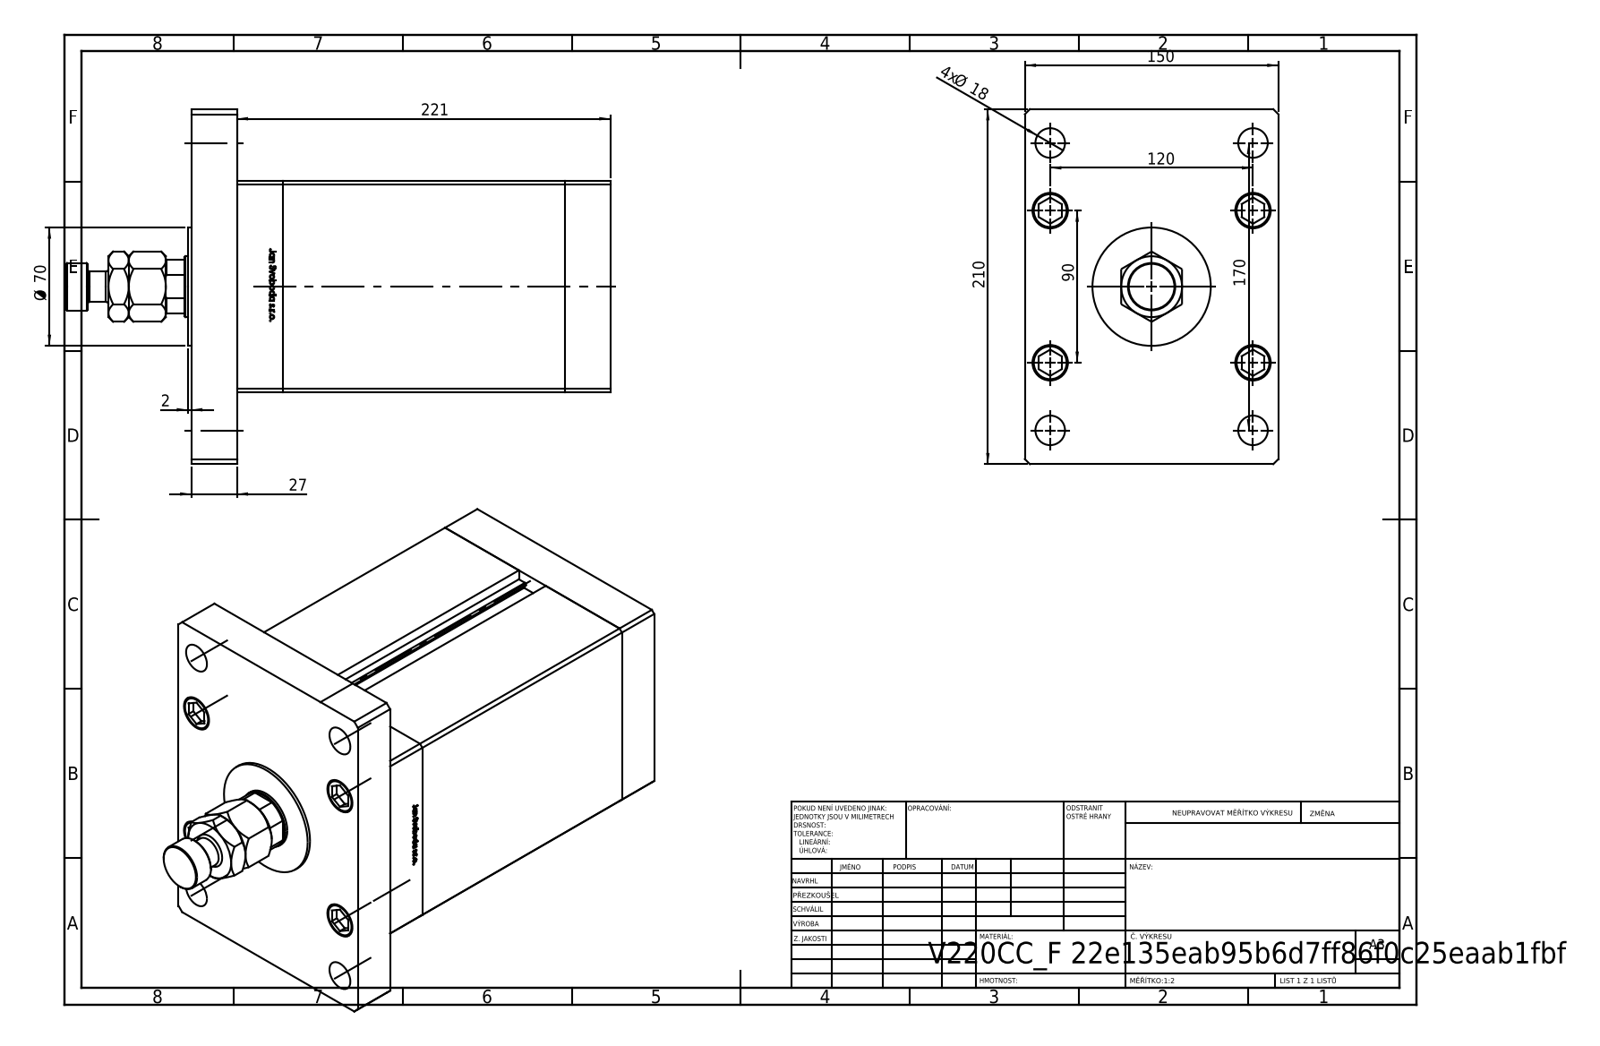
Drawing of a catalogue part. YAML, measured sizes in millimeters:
part_name: "V220C_FRONT_F; ALLEN BOLT; V220C_F; V220C_VC_F (+3 more)"
step_written_by: "SolidWorks 2019 (CONFIG_CONTROL_DESIGN)"
units: millimeters
bodies: {solids: 20, faces: 1362, planar: 533, cylindrical: 191, other: 638}
overall_size: [322, 210, 150]
volume: 4412000
surface_area: 480880
round_holes:
  - {diameter: 17.5, count: 9}
  - {diameter: 22, count: 5}
  - {diameter: 16, count: 4}
  - {diameter: 21, count: 4}
  - {diameter: 2, count: 2}
  - {diameter: 13.16, count: 2}
  - {diameter: 25.5, count: 1}
  - {diameter: 36, count: 1}
  - {diameter: 37.5, count: 1}
round_bosses_or_shafts:
  - {diameter: 8, count: 9}
  - {diameter: 21, count: 5}
  - {diameter: 80, count: 1}
  - {diameter: 70, count: 1}
  - {diameter: 28, count: 1}
  - {diameter: 18, count: 1}
partial_cylinders:
  - {radius: 0.93, count: 2}
  - {radius: 17.5, count: 1}
face_to_face_distances: [27, 194, 221, 150, 125, 167, 54, 248, 33.5, 6.5]
hole_center_spacings: [51, 40, 75, 104.04, 120, 126.49, 130, 176.92]
